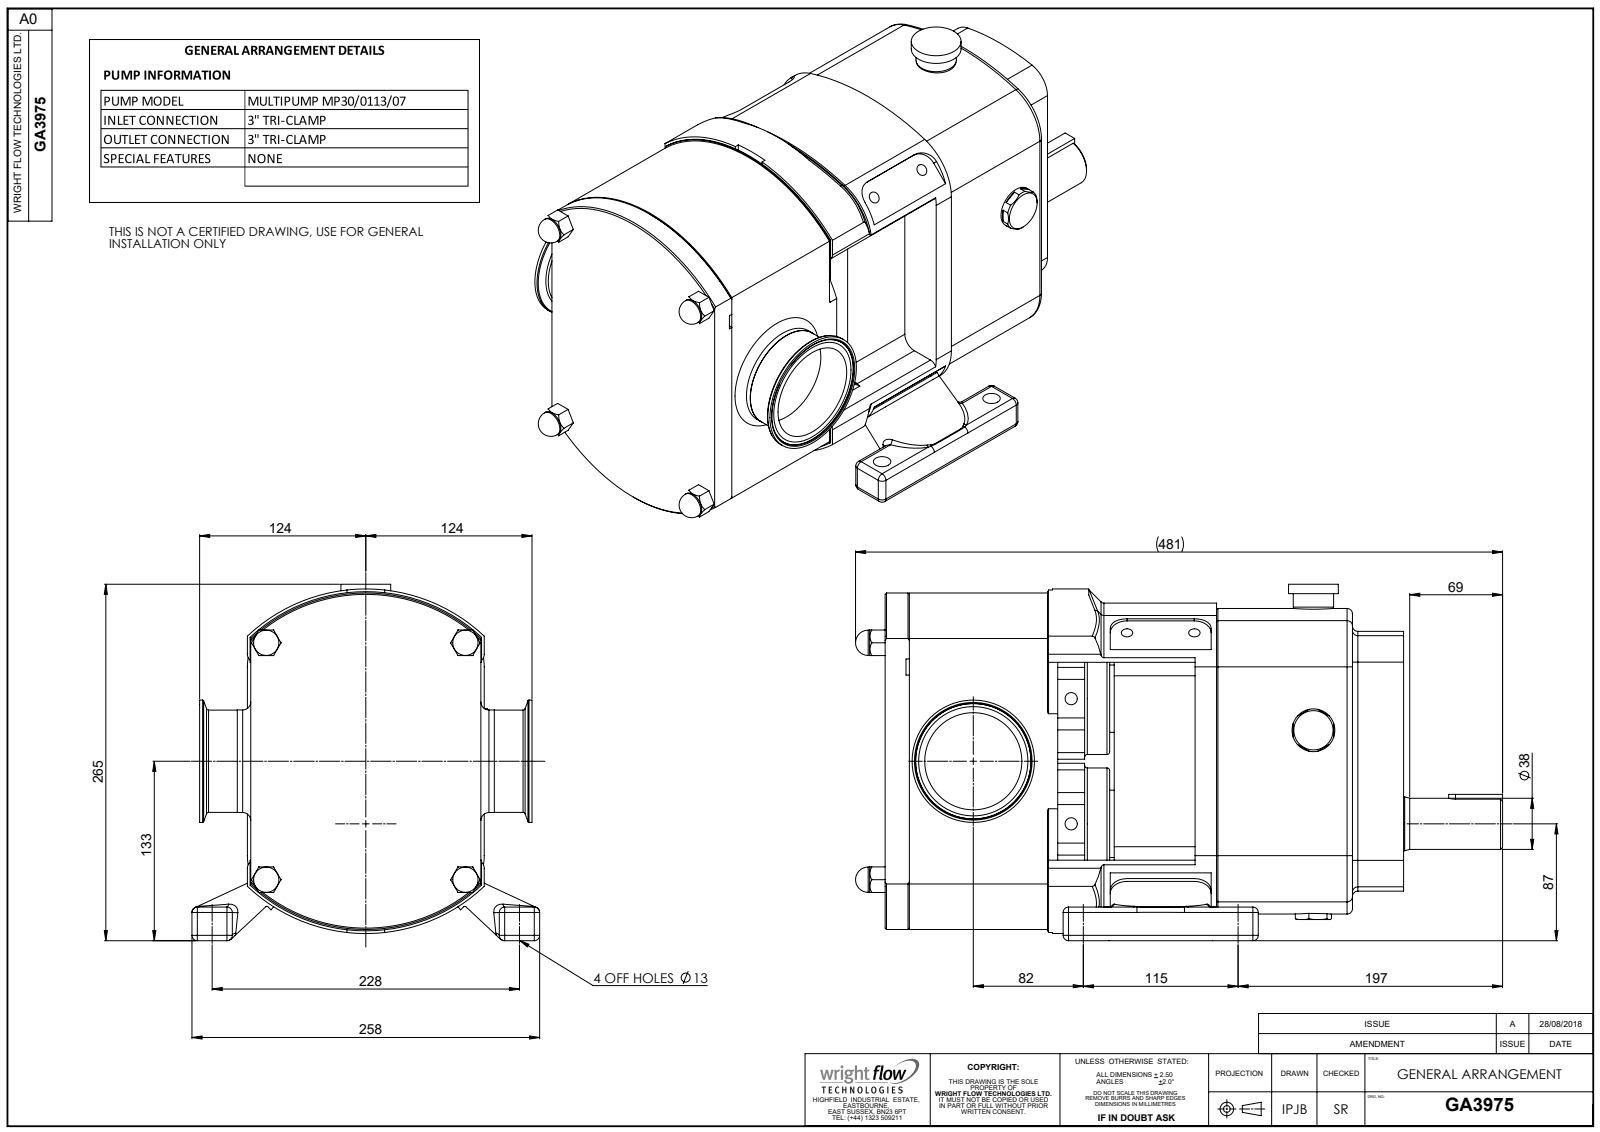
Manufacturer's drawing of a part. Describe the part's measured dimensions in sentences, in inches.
The part is named "Copy of CP30-0113-07 H B^GA3975; GA3975; Copy of Z94-5121-55 - 3 INCH^GA3975". Its 3-D file was written by "SolidWorks 2023 (AUTOMOTIVE_DESIGN)". It is 3 solids with 725 faces: 265 planar, 237 cylindrical and 223 other. Overall it measures 18.93 by 10.427 by 10.172 inches. Its volume is 787.8 cubic inches and its surface area 873.5 square inches. Round holes: 4 of diameter 0.335, 4 of diameter 0.398, 4 of diameter 0.512, 2 of diameter 0.358, 1 of diameter 1.378, 1 of diameter 2.843. Round bosses or shafts: 4 of diameter 0.74, 2 of diameter 3.268, 2 of diameter 1.969, 1 of diameter 3.579, 1 of diameter 3, 1 of diameter 2.992, 1 of diameter 1.575, 1 of diameter 1.496. Partial cylindrical surfaces (rounded edges, fillets, slot ends): 44 of radius 0.157, 16 of radius 0.039, 12 of radius 0.394, 10 of radius 0.236, 4 of radius 0.492, 4 of radius 0.495, 4 of radius 0.496, 4 of radius 0.787. The main face-to-face distances are 0.059, 6.673, 5.472, 1.496, 6.702, 1.142, 8.467, 15.169, 6.732, 1.201. The hole center spacings are 2.506, 1.97, 3.399, 3.543, 4.528, 5.007, 8.095, 8.991.
